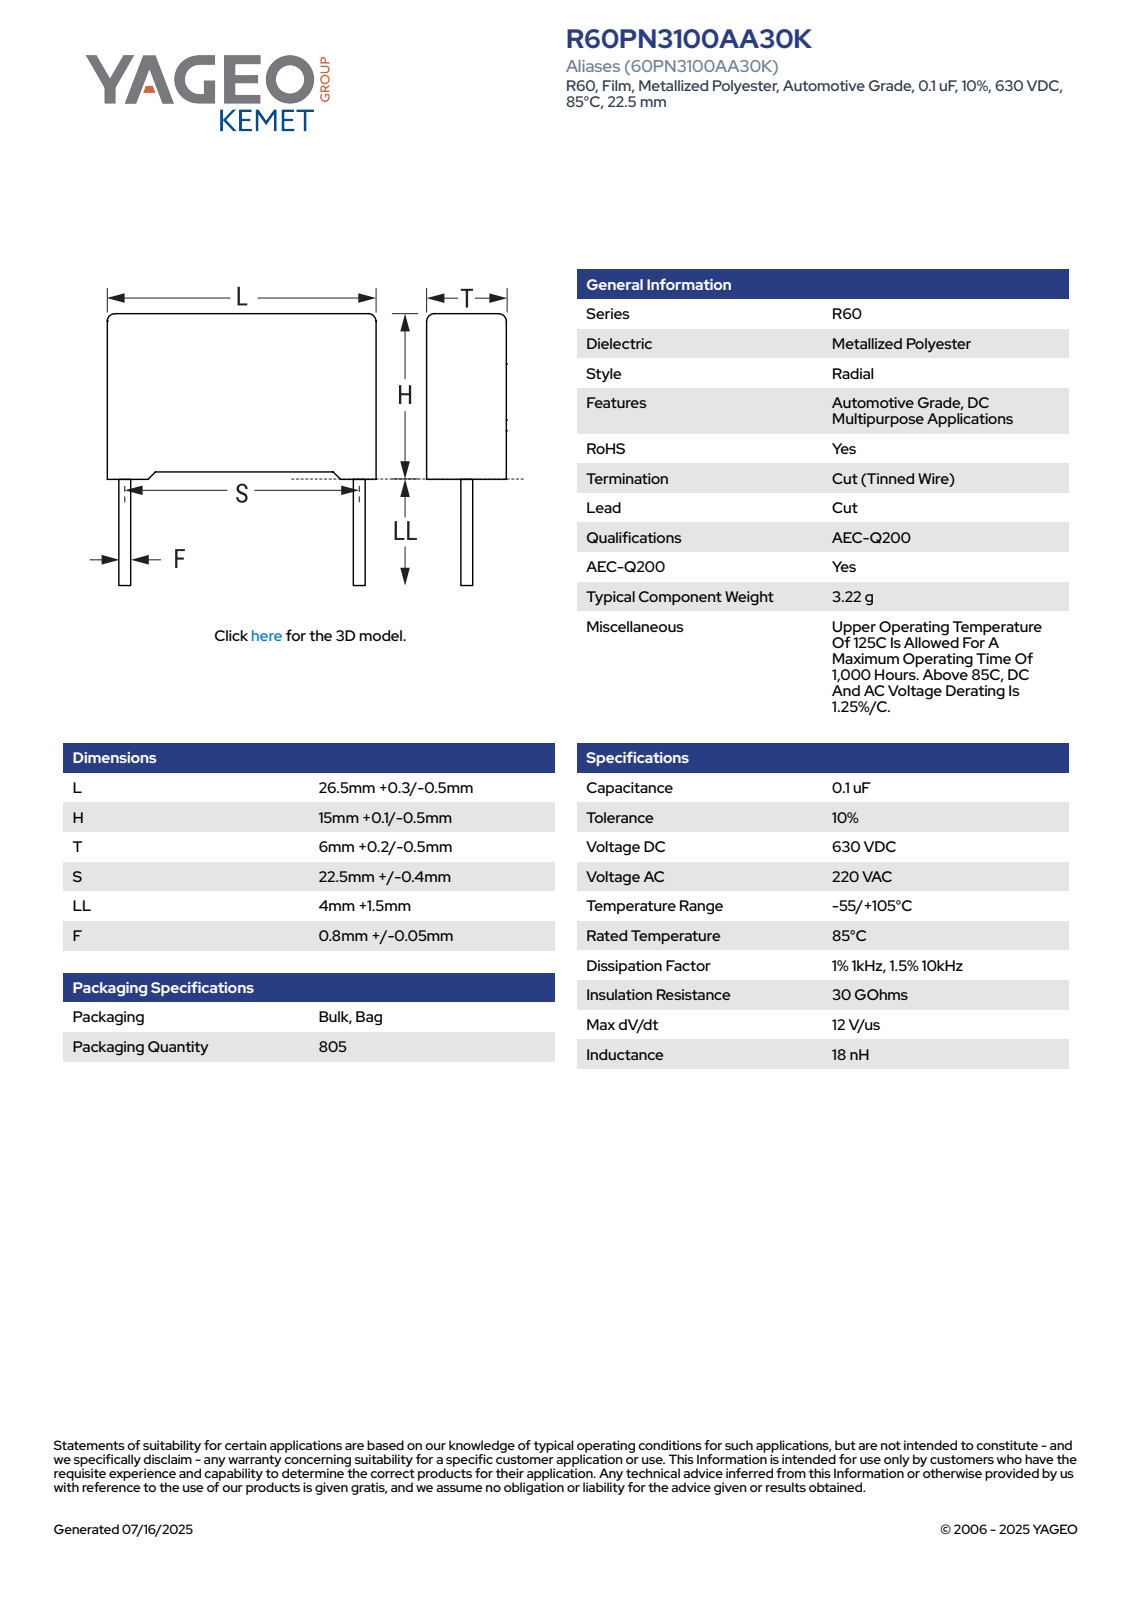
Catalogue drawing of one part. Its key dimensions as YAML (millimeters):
part_name: "CFR_RB2_26.5X15X6_L26.8H15.1T6.2S22.5LL5.5F0.85"
step_written_by: "SolidWorks 2021 (AUTOMOTIVE_DESIGN)"
units: millimeters
bodies: {solids: 4, faces: 85, planar: 77, cylindrical: 8, other: 0}
overall_size: [26.8, 20.6, 6.21]
volume: 2413
surface_area: 1408
round_bosses_or_shafts:
  - {diameter: 0.85, count: 2}
partial_cylinders:
  - {radius: 0.5, count: 4}
face_to_face_distances: [6.2, 14.35, 26.8, 14.58, 0.89, 0.52, 0.75, 15.1, 5.31, 4.42]
